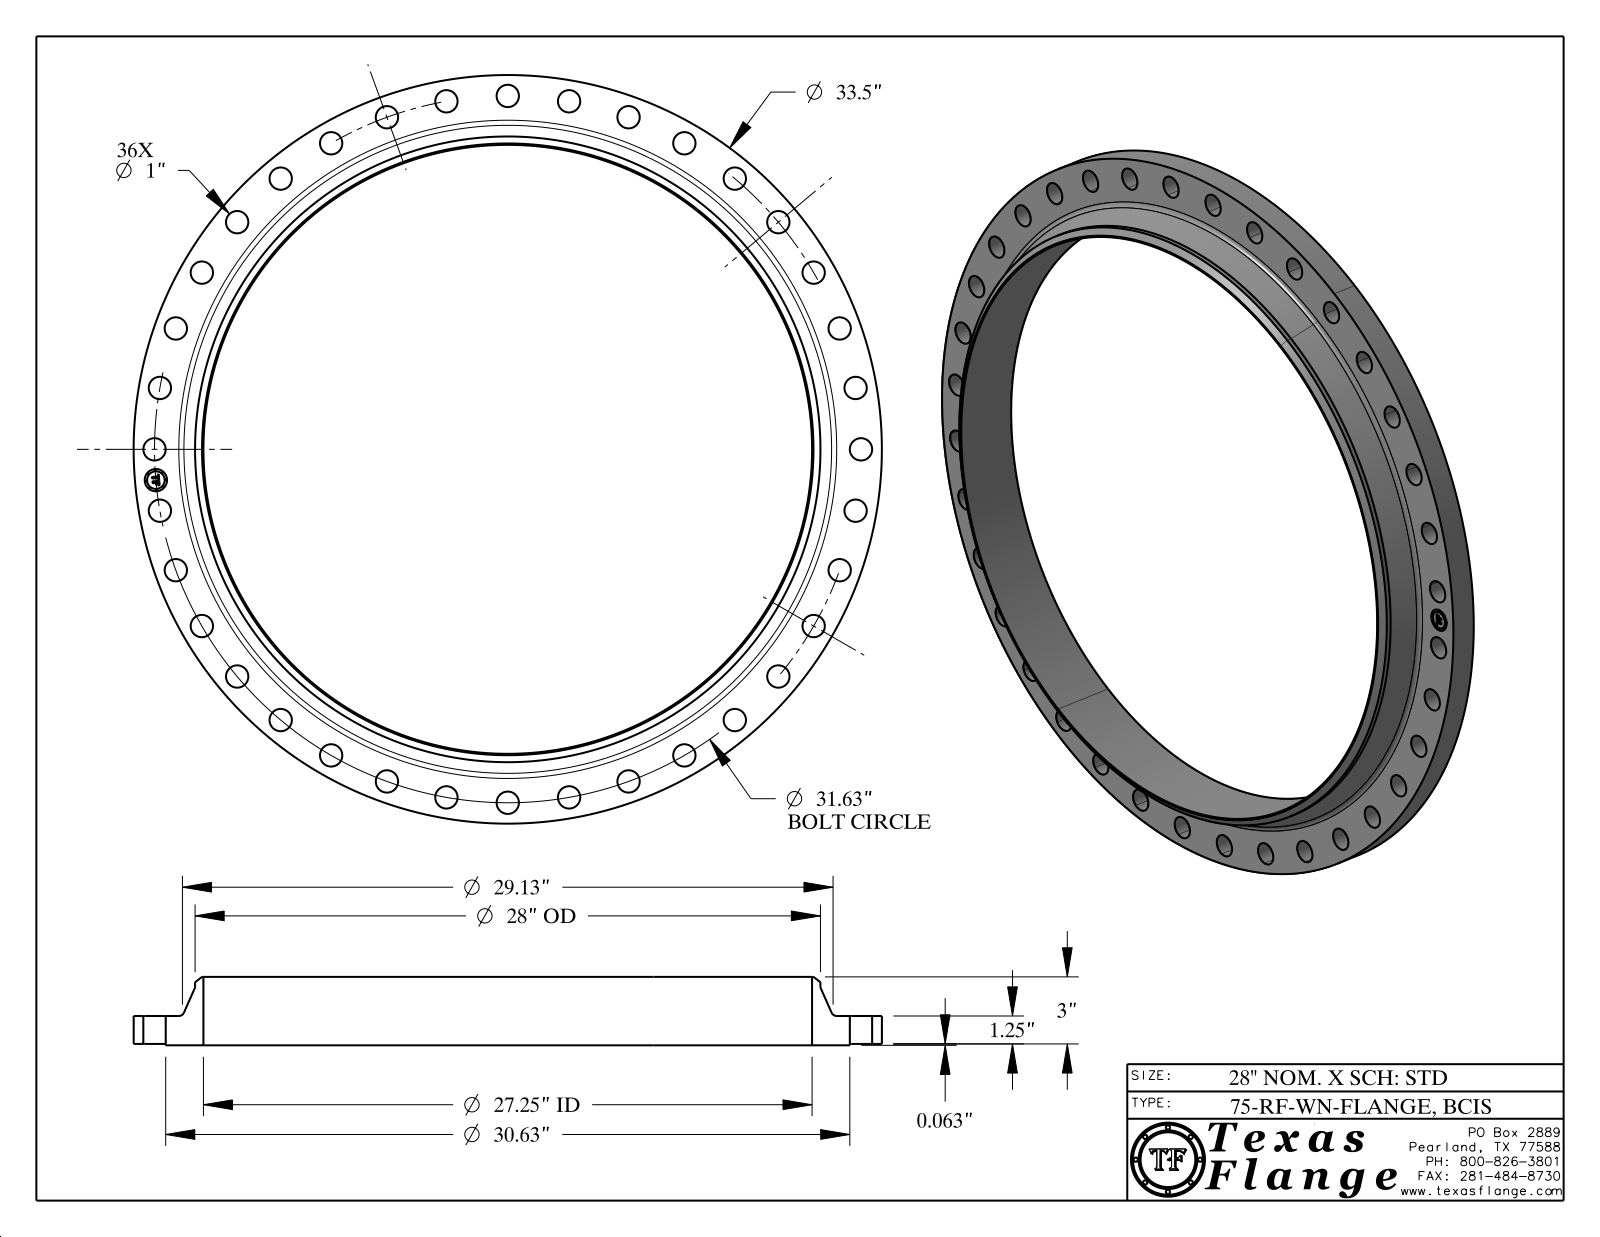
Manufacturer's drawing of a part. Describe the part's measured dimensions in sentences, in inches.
The part is named "75-RF-WN, BCIS". Its 3-D file was written by "CATIA V5 STEP AP214 (AUTOMOTIVE_DESIGN)". It is 1 solid with 475 faces: 369 planar, 100 cylindrical and 6 other. Overall it measures 33.5 by 33.5 by 3.063 inches. Its volume is 433.2 cubic inches and its surface area 1 180 square inches. Round holes: 37 of diameter 1, 1 of diameter 27.25. Round bosses or shafts: 8 of diameter 0.061, 1 of diameter 33.5, 1 of diameter 30.63, 1 of diameter 28, 1 of diameter 0.788. The main face-to-face distances are 1.313, 0.063, 1.25, 3.063, 3, 1.75, 0.015, 1.298, 1.235, 1.765. The hole center spacings are 15.815, 10.818, 28.667, 29.722, 5.493, 13.367, 22.366, 2.757.
